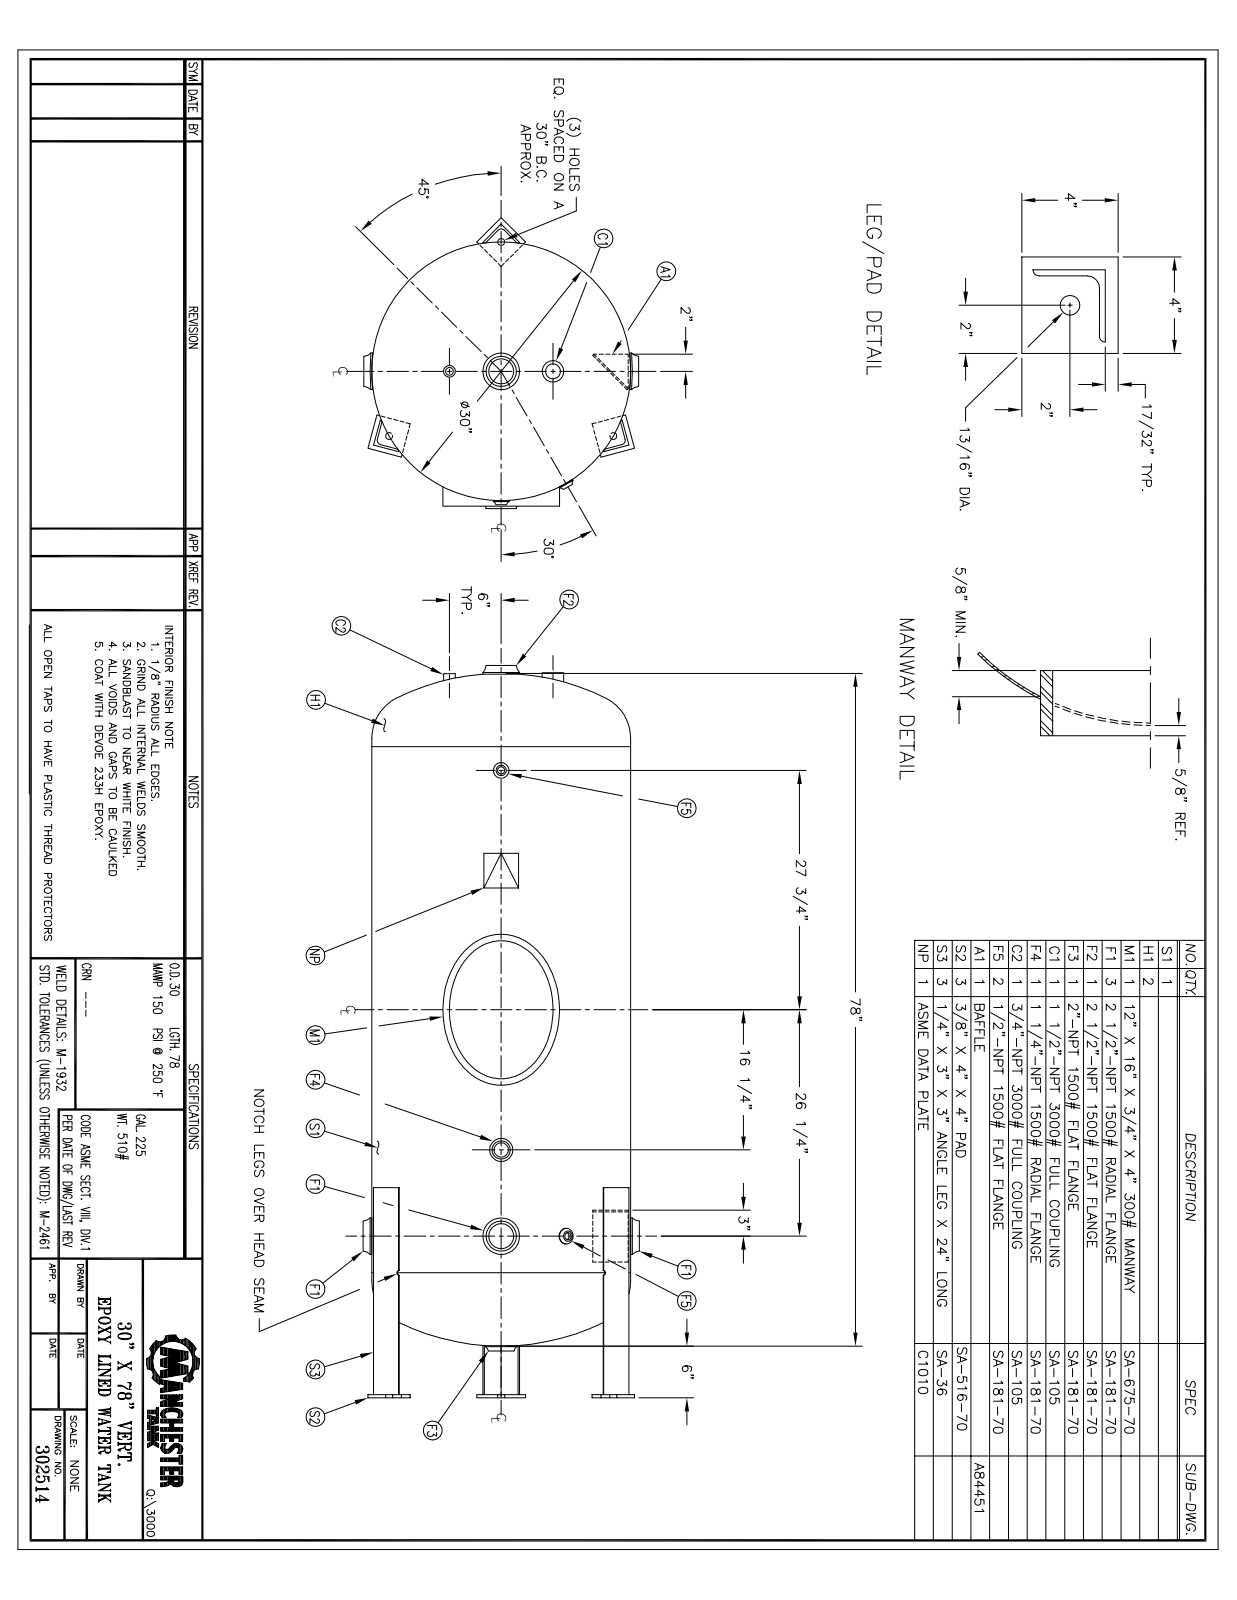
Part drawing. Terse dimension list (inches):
name: 302514
written by: SolidWorks 2011 (CONFIG_CONTROL_DESIGN)
unit: in
bodies: 0 solids, 334 faces (126 planar, 108 cylindrical, 100 other)
size: 84.812 × 38.825 × 32.01
holes: 3× ⌀0.813, 3× ⌀2.875, 2× ⌀0.84, 1× ⌀1.05, 1× ⌀1.5, 1× ⌀1.66, 1× ⌀1.9, 1× ⌀2.375, 1× ⌀2.625, 1× ⌀29.256, 1× ⌀29.628, 1× ⌀29.638
bosses: 2× ⌀4.25, 2× ⌀1.813, 2× ⌀1, 1× ⌀30, 1× ⌀29.63, 1× ⌀4.062, 1× ⌀3.5, 1× ⌀3.313
rounds: 11× R0.25, 4× R1.318, 3× R0.474, 3× R0.698, 2× R0.375, 1× R0.187, 1× R5.917, 1× R6
face distances: 0.224, 0.375, 3, 3.248, 3.023, 25.289, 28.289, 32.711, 35.711, 7.422
hole spacings: 15, 6, 10.253, 16.156, 20.418, 25.981, 10, 12
